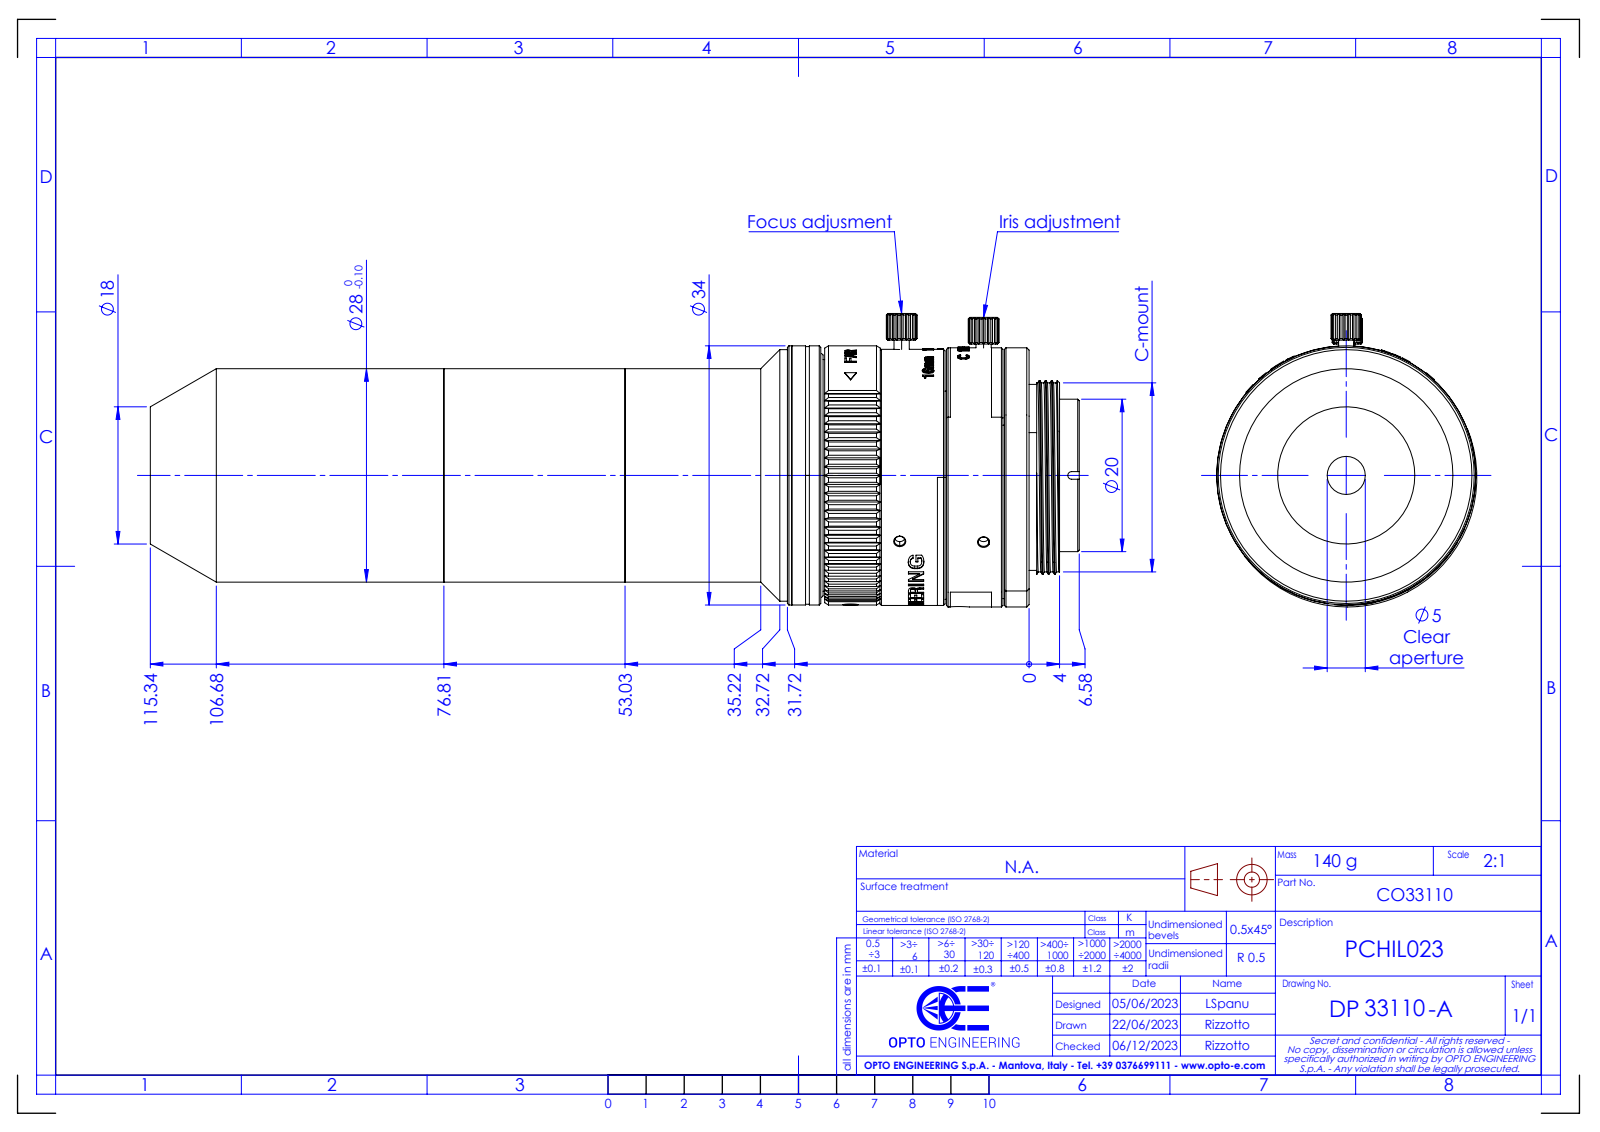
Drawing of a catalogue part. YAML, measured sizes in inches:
part_name: "DP33110-A_PCHIL023"
step_written_by: "SolidWorks 2021 (CONFIG_CONTROL_DESIGN)"
units: inches
bodies: {solids: 0, faces: 916, planar: 402, cylindrical: 243, other: 271}
overall_size: [4.8, 1.516, 1.344]
round_holes:
  - {diameter: 0.055, count: 4}
  - {diameter: 0.083, count: 2}
  - {diameter: 0.079, count: 1}
  - {diameter: 0.102, count: 1}
  - {diameter: 0.197, count: 1}
  - {diameter: 0.551, count: 1}
  - {diameter: 0.827, count: 1}
  - {diameter: 0.843, count: 1}
  - {diameter: 1.254, count: 1}
round_bosses_or_shafts:
  - {diameter: 1.339, count: 2}
  - {diameter: 1.331, count: 1}
  - {diameter: 1.323, count: 1}
  - {diameter: 1.299, count: 1}
  - {diameter: 1.26, count: 1}
  - {diameter: 1.102, count: 1}
  - {diameter: 1, count: 1}
  - {diameter: 0.961, count: 1}
partial_cylinders:
  - {radius: 0.039, count: 2}
  - {radius: 0.079, count: 2}
  - {radius: 0.673, count: 2}
  - {radius: 0.02, count: 1}
  - {radius: 0.041, count: 1}
  - {radius: 0.327, count: 1}
  - {radius: 0.374, count: 1}
  - {radius: 0.472, count: 1}
face_to_face_distances: [4.541, 1.517, 3.024, 2.453, 0.936, 2.088, 3.728, 2.211, 1.275, 0.813]
hole_center_spacings: [0.549, 0.433, 0.559, 0.952]
